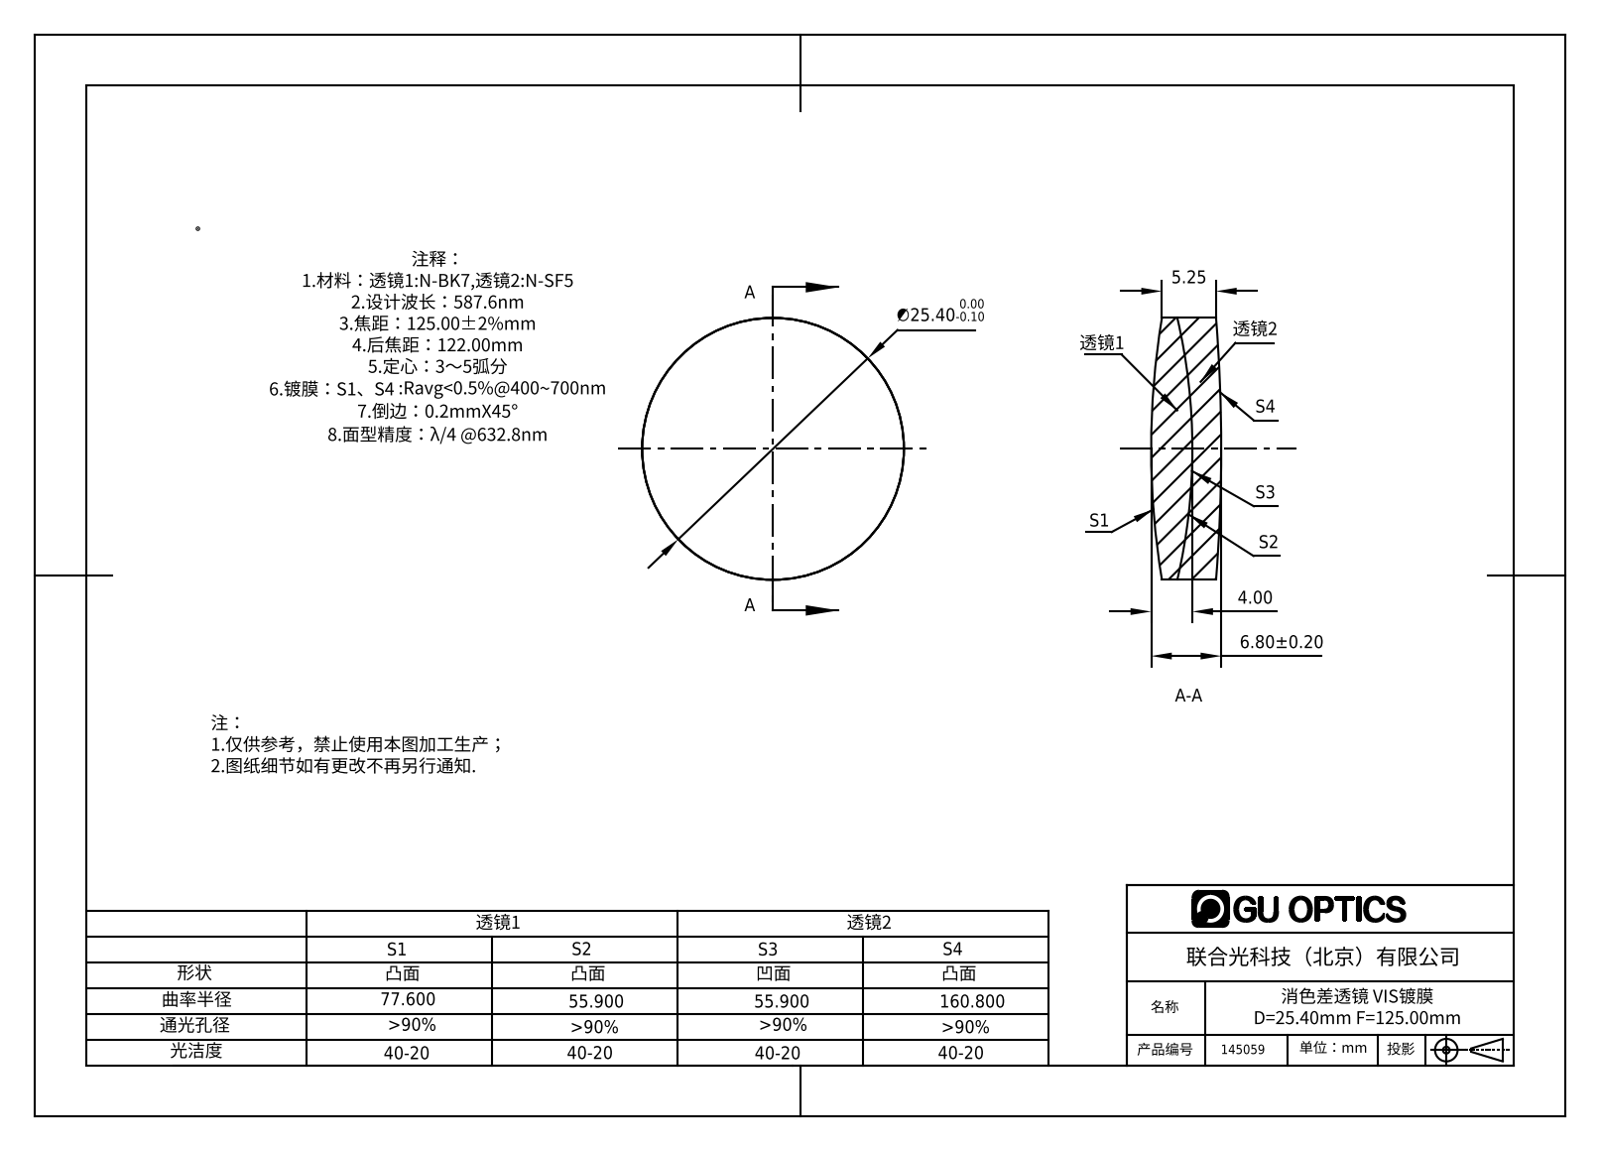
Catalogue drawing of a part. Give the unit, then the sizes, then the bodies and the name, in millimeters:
Units: millimetres
Overall size (bounding box): 25.4 × 25.4 × 6.8
Round bosses / shafts (diameter × count): ⌀25.4 ×1
Volume: 3 054 mm³ · Surface area: 2 464 mm²
Bodies: 2 solids, 12 faces (0 planar, 4 cylindrical, 8 other)
Part name (STEP PRODUCT): 145059
STEP written by: SolidWorks 2016 (AUTOMOTIVE_DESIGN)
